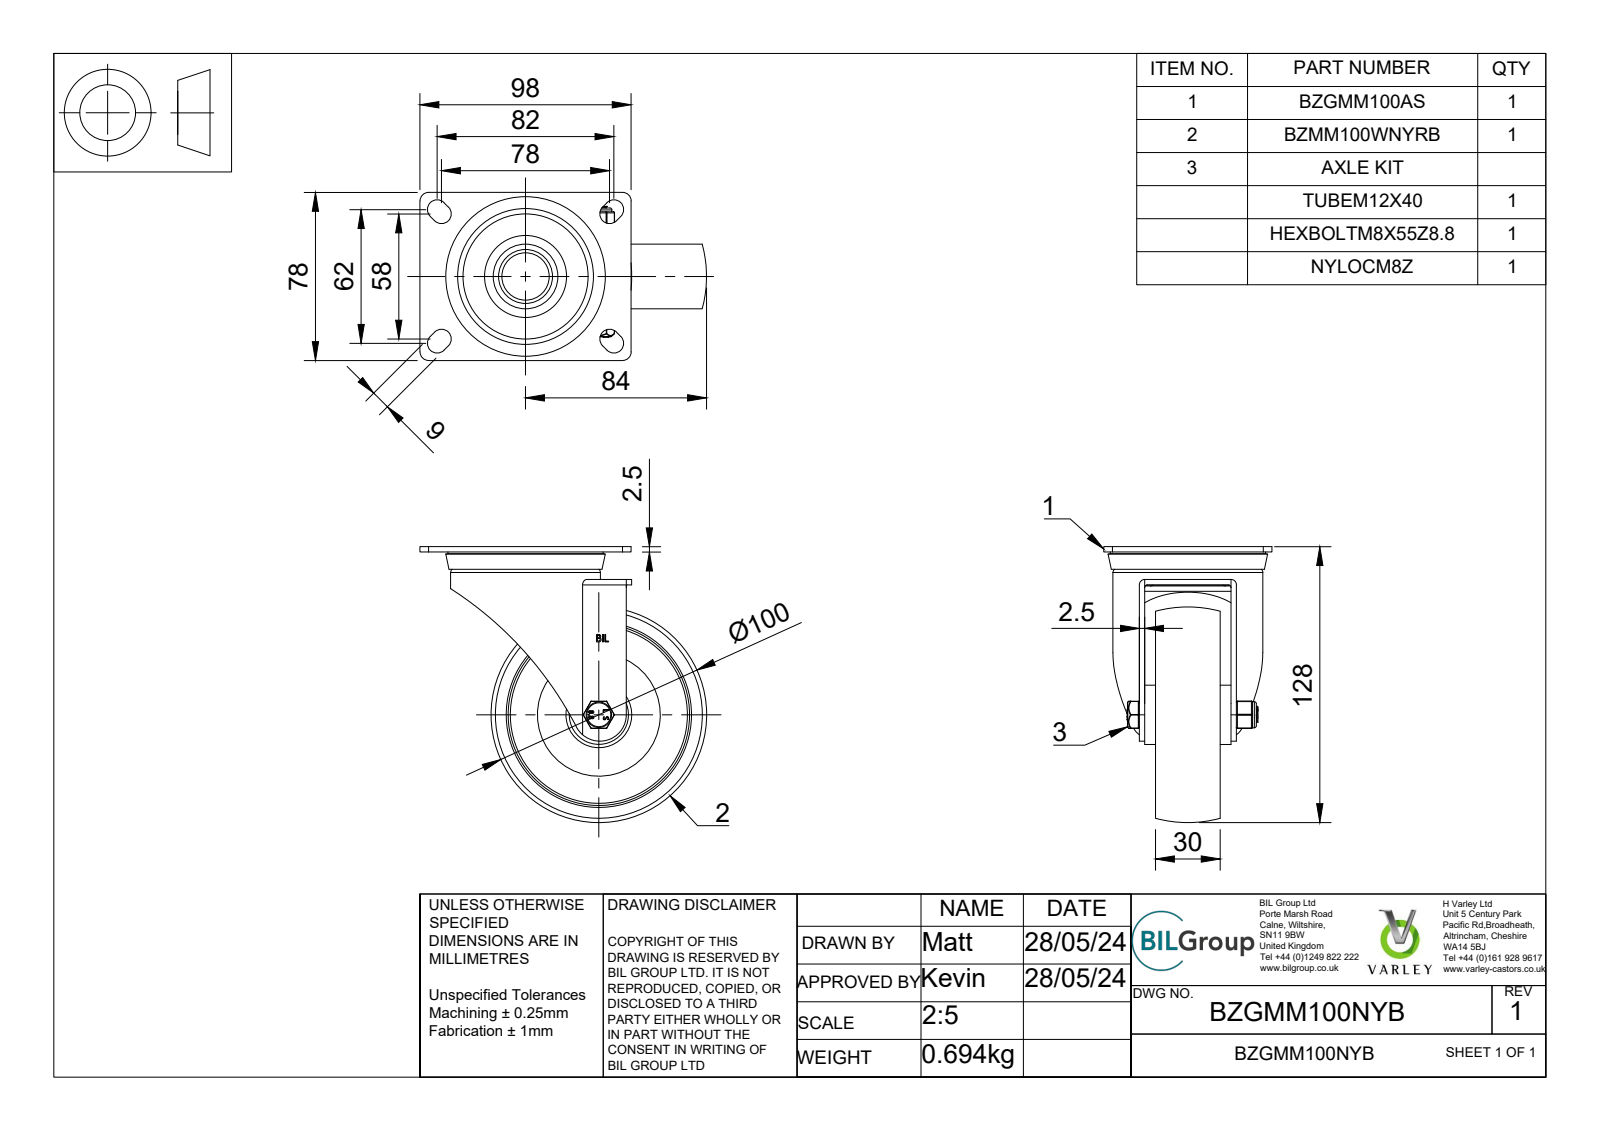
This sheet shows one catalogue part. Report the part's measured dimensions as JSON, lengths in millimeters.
{"part_name": "BZGMM100NYB v3; BZGMM100AS - 2 v1; ZINC PLATED, PRESSED STEEL TOP PLATE; ZINC PLATED, PRESSED STEEL TOP PLATE Geometry (+7 more)", "step_written_by": "Autodesk Translation Framework v13.14.0.145 (AUTOMOTIVE_DESIGN)", "units": "millimeters", "bodies": {"solids": 46, "faces": 490, "planar": 191, "cylindrical": 179, "other": 120}, "overall_size": [133, 128, 78], "volume_mm3": 200207, "surface_area_mm2": 101916, "round_holes": [[0.66, 2], [8, 1], [8.2, 1], [8.4, 1], [8.6, 1], [12.2, 1], [12.5, 1], [20, 1], [26, 1], [30, 1], [64.5, 1]], "round_bosses_or_shafts": [[3.75, 8], [69.5, 1], [47, 1], [27.5, 1], [25, 1], [19.5, 1], [12.1, 1], [11.9, 1]], "partial_cylinders_radius": [[0.5, 18], [0.25, 12], [4.5, 8], [0.33, 4], [0.64, 4], [1.25, 4], [4, 4], [0.63, 2]], "face_to_face_distances": [2.5, 7.5, 18.75, 16.25, 23.75, 5, 11.25, 37.5, 3, 35], "hole_center_spacings": [3.22, 2.49]}
